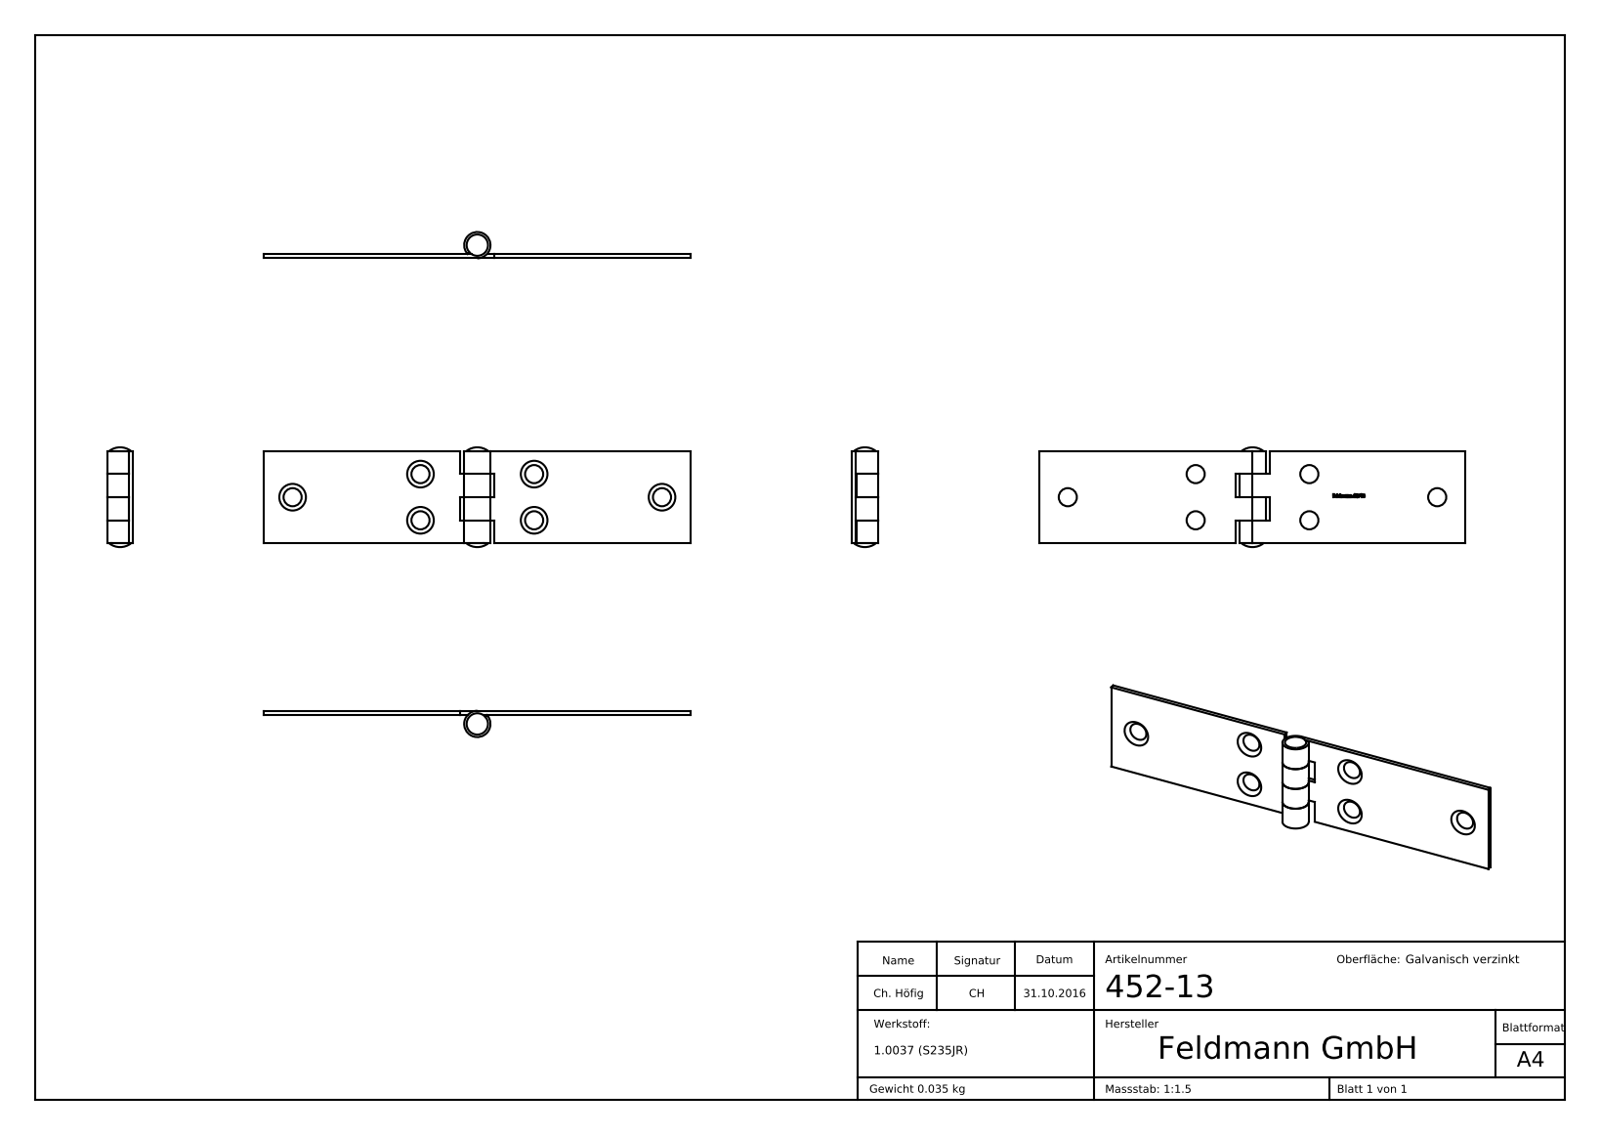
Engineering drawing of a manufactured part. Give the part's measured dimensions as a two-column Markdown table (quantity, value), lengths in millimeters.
| quantity | value |
| --- | --- |
| part name | 452-13 Teil2; 452-13 Teil1; 452-13; 452-13 Teil3 |
| STEP written by | SolidWorks 2018 (CONFIG_CONTROL_DESIGN) |
| units | millimeters |
| bodies | 3 solids, 229 faces (136 planar, 9 cylindrical, 84 other) |
| overall size | 120 × 28.1 × 7.4 |
| volume | 4 433 mm³ |
| surface area | 7 769 mm² |
| round holes (diameter × count) | 5 × 1 |
| round bosses / shafts (diameter × count) | 7.4 × 1 |
| main face-to-face distances | 1.2, 6.5, 26, 13, 19.5, 55.2, 64.8, 120, 6.55, 13.05 |
